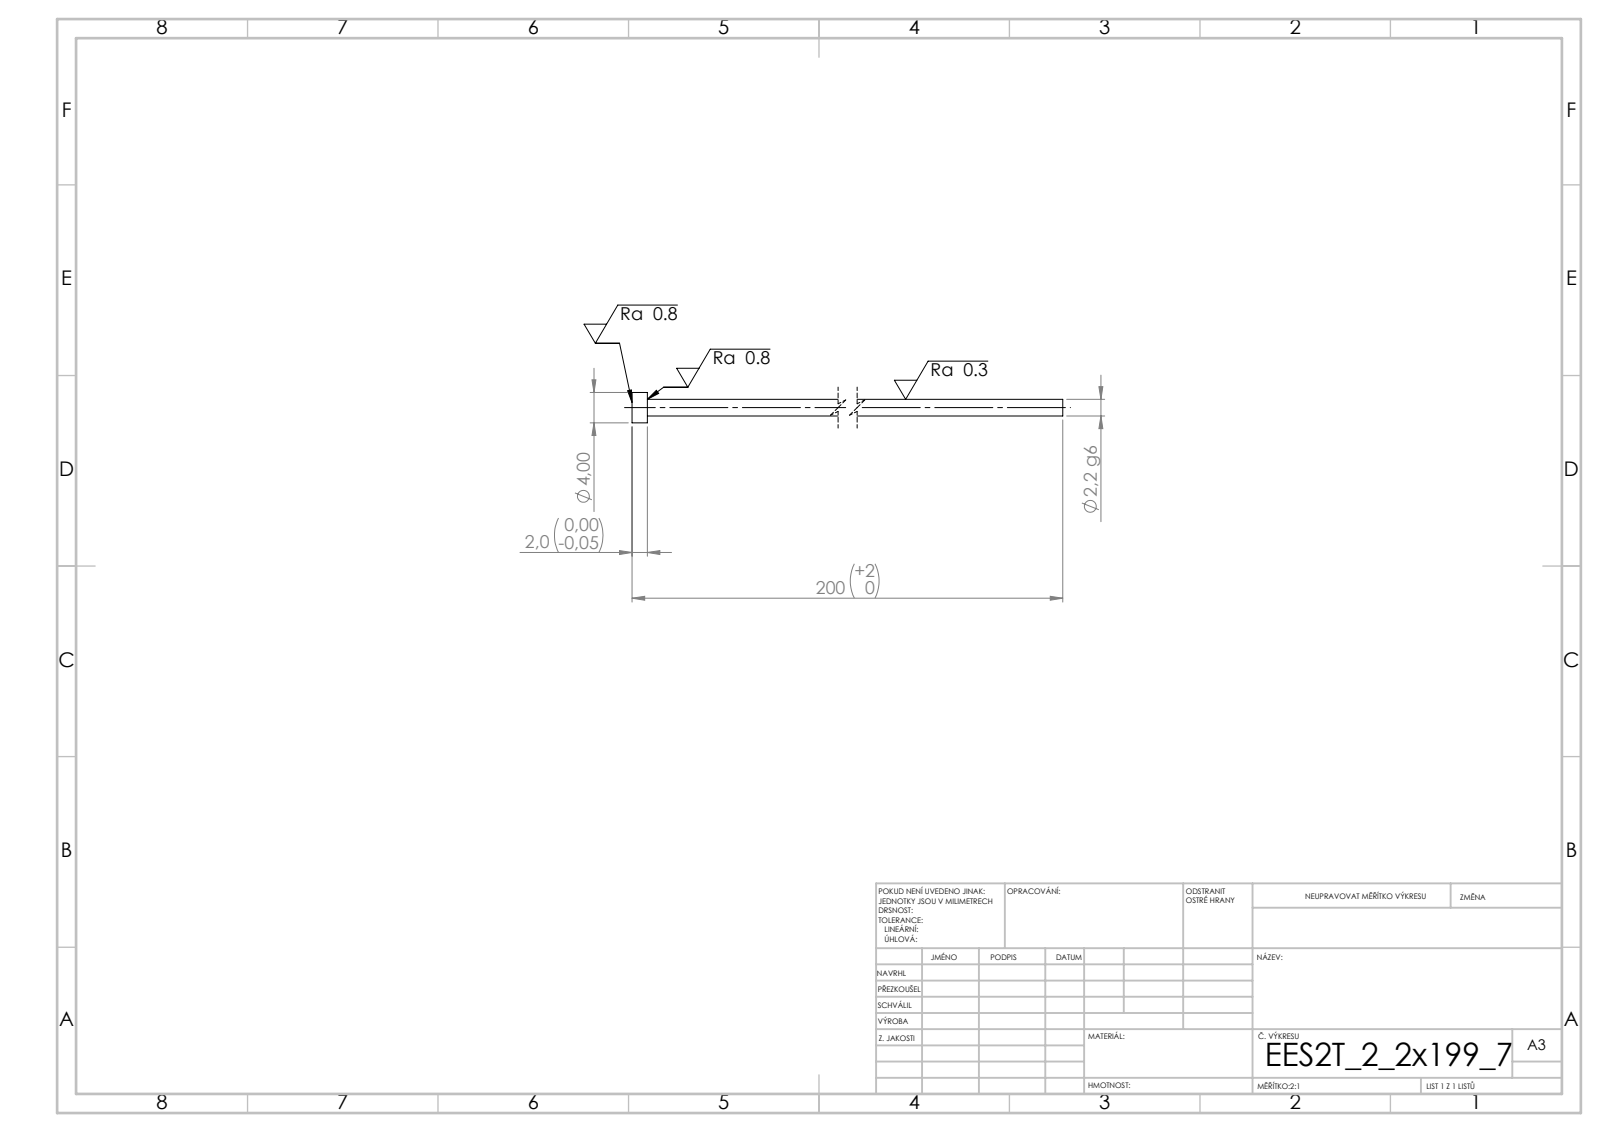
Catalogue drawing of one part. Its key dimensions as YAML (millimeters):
step_written_by: "SolidWorks 2019 (CONFIG_CONTROL_DESIGN)"
units: millimeters
bodies: {solids: 1, faces: 7, planar: 3, cylindrical: 4, other: 0}
overall_size: [199.7, 4, 4]
volume: 777
surface_area: 1417
round_bosses_or_shafts:
  - {diameter: 4, count: 1}
  - {diameter: 2.2, count: 1}
face_to_face_distances: [2, 199.7, 197.7]
